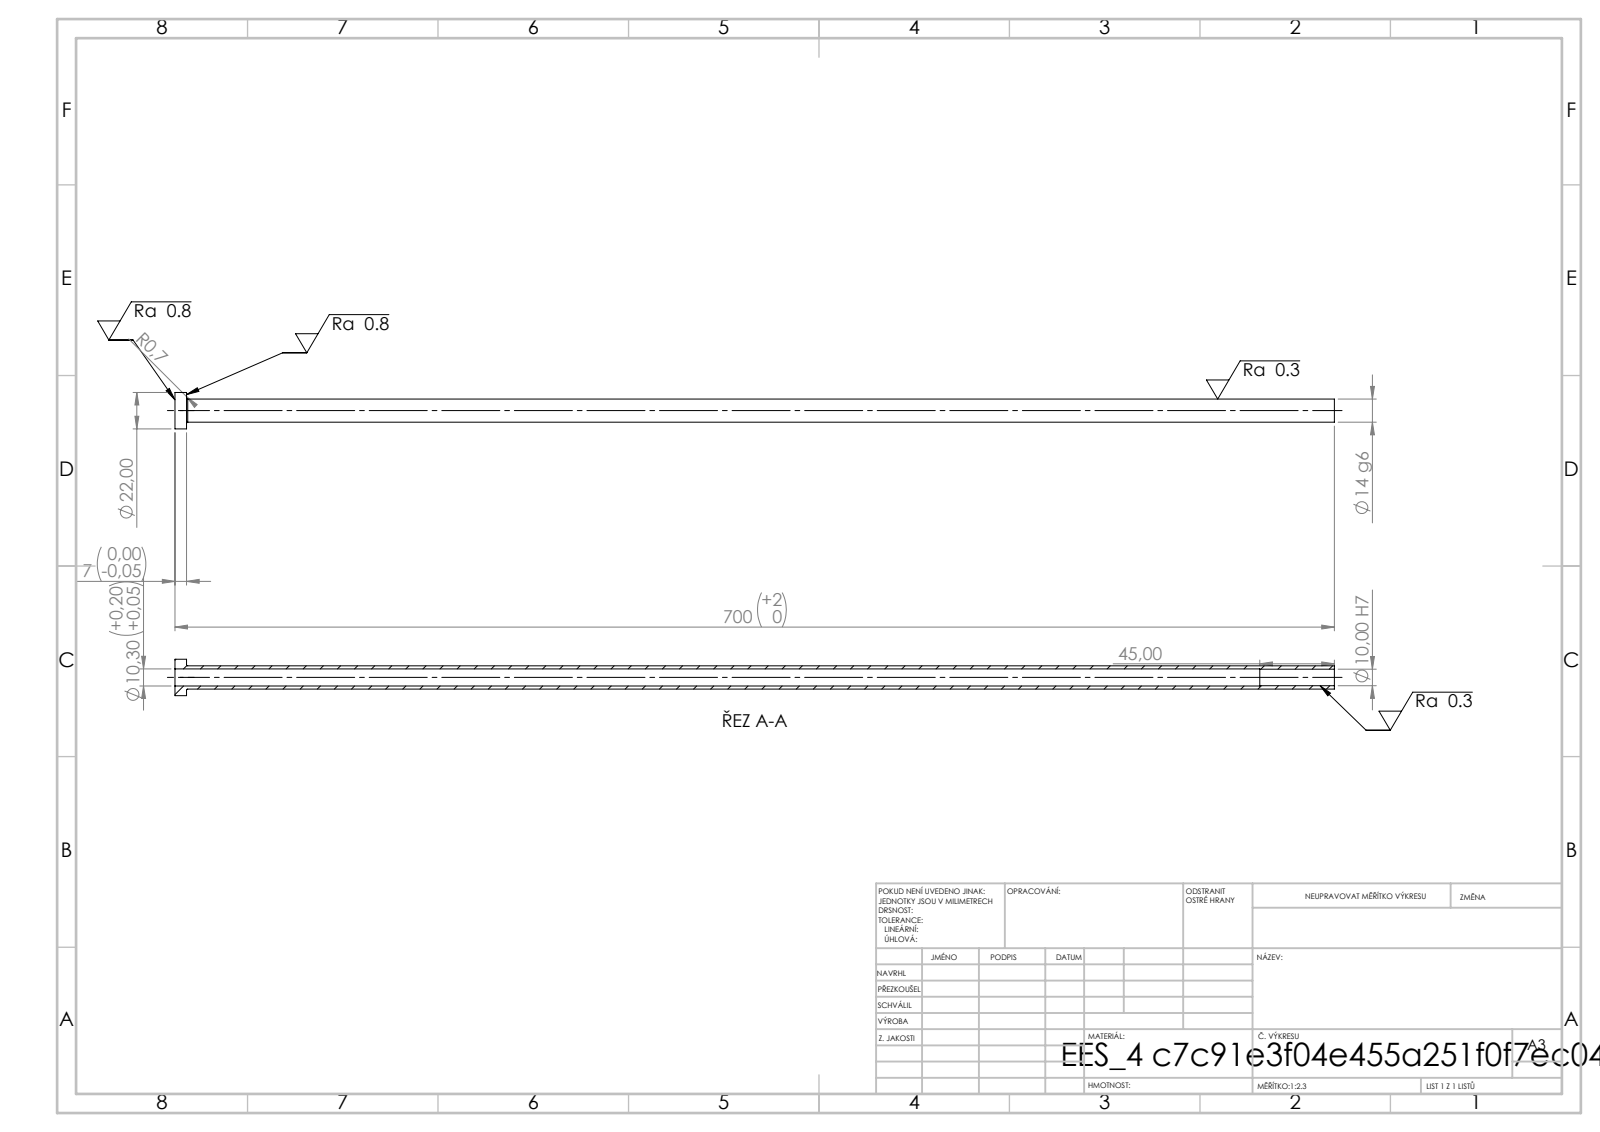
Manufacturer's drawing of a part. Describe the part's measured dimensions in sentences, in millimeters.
Its 3-D file was written by "SolidWorks 2019 (CONFIG_CONTROL_DESIGN)". It is 1 solid with 14 faces: 4 planar, 8 cylindrical and 2 other. Overall it measures 700 by 22 by 22 millimeters. Its volume is 51 234 cubic millimeters and its surface area 54 162 square millimeters. Round holes: 1 of diameter 10, 1 of diameter 10.3. Round bosses or shafts: 1 of diameter 22, 1 of diameter 14. The main face-to-face distances are 7, 700, 693, 655, 648, 45.
